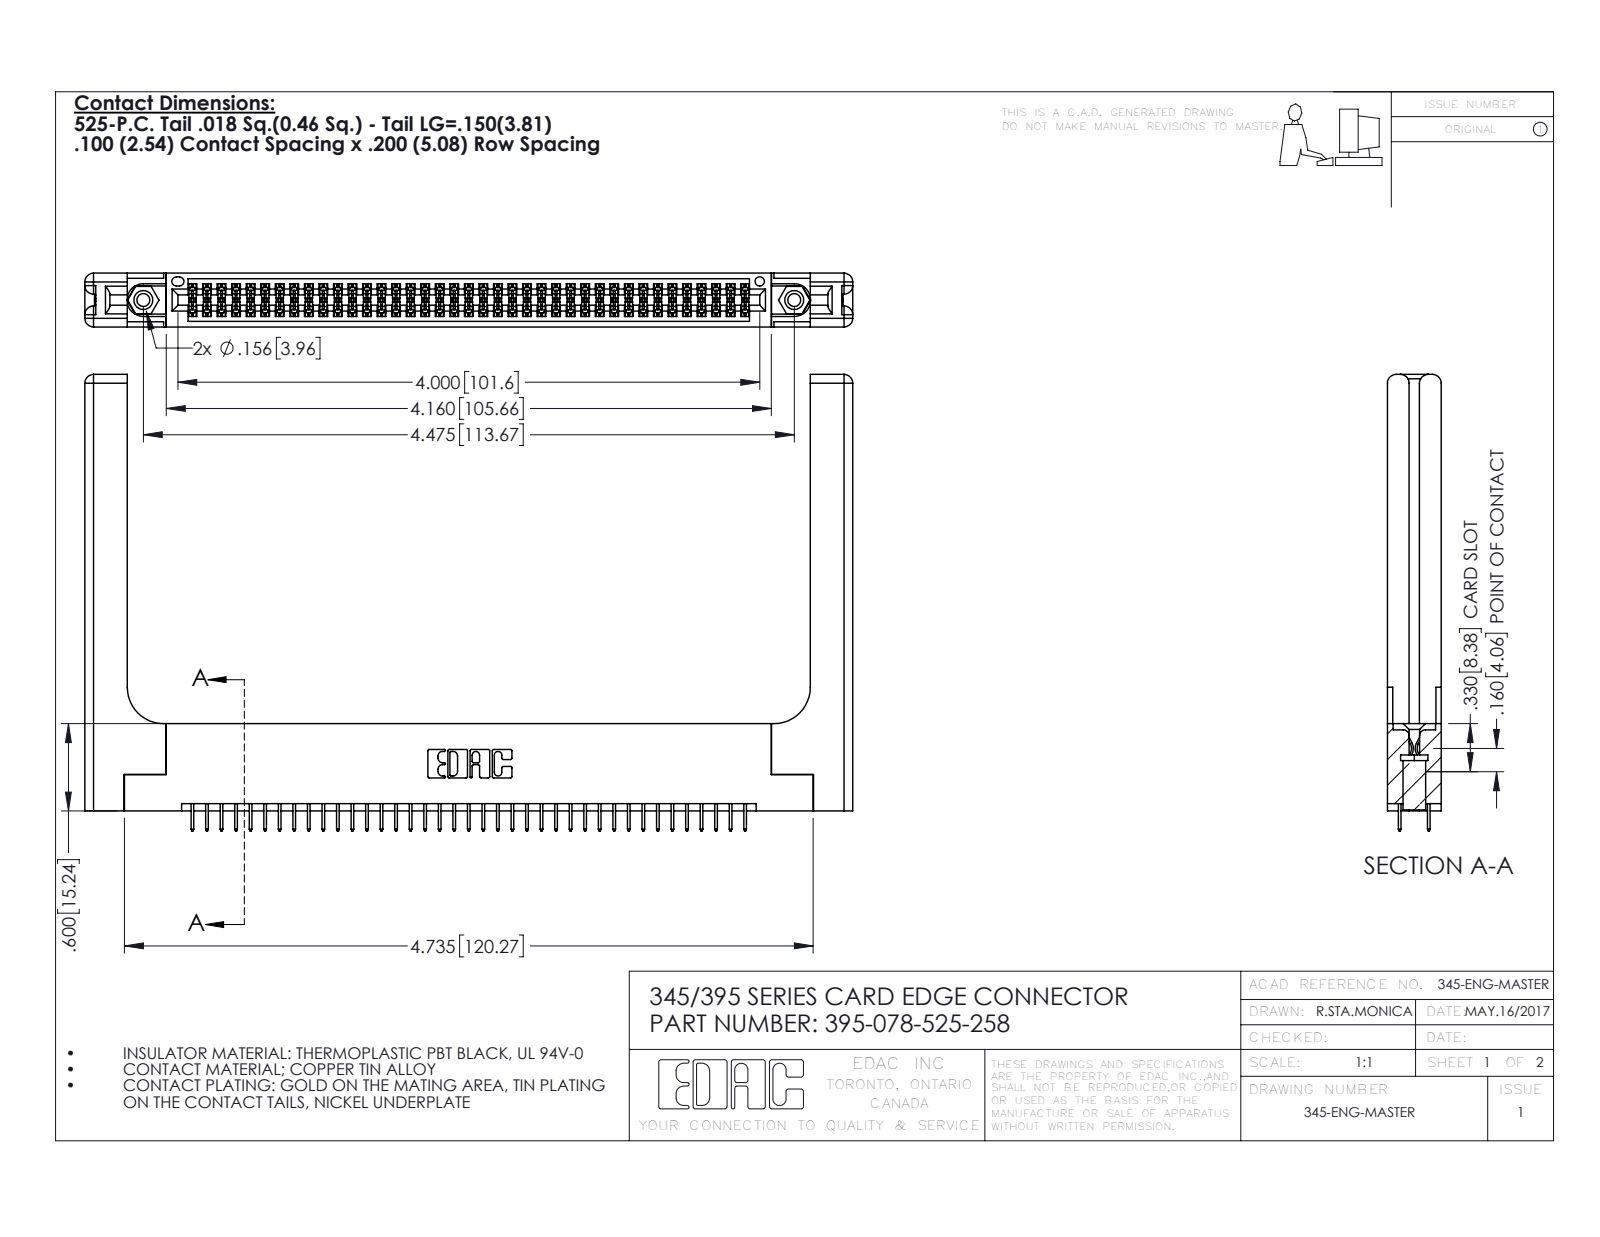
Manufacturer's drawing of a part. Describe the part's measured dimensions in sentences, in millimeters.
The part is named "345-220-058_345-220-058; 345 Part_Flush Mounting Lugs - 0.156 Dia-TH; 345-292-001_345-293-125; 345-250-001_345-250-001-102 (+1 more)". Its 3-D file was written by "SolidWorks 2020 (CONFIG_CONTROL_DESIGN)". It is 83 solids with 4594 faces: 3270 planar, 1264 cylindrical and 60 other. Overall it measures 134.1 by 79.7 by 9.4 millimeters. Its volume is 21 350 cubic millimeters and its surface area 23 640 square millimeters. Round holes: 2 of diameter 2.3, 2 of diameter 3.2, 2 of diameter 4, 1 of diameter 1.6. Round bosses or shafts: 2 of diameter 3.9. Partial cylindrical surfaces (rounded edges, fillets, slot ends): 117 of radius 0.2, 22 of radius 0.3, 16 of radius 1.5, 6 of radius 0.2, 6 of radius 0.8, 3 of radius 0.7, 2 of radius 0.4, 2 of radius 0.5. The main face-to-face distances are 9.4, 1.8, 7.6, 5.1, 2.5, 6.9, 0.6, 5.7, 3.8, 3.8. The hole center spacings are 6.9, 107.7, 113.7.
